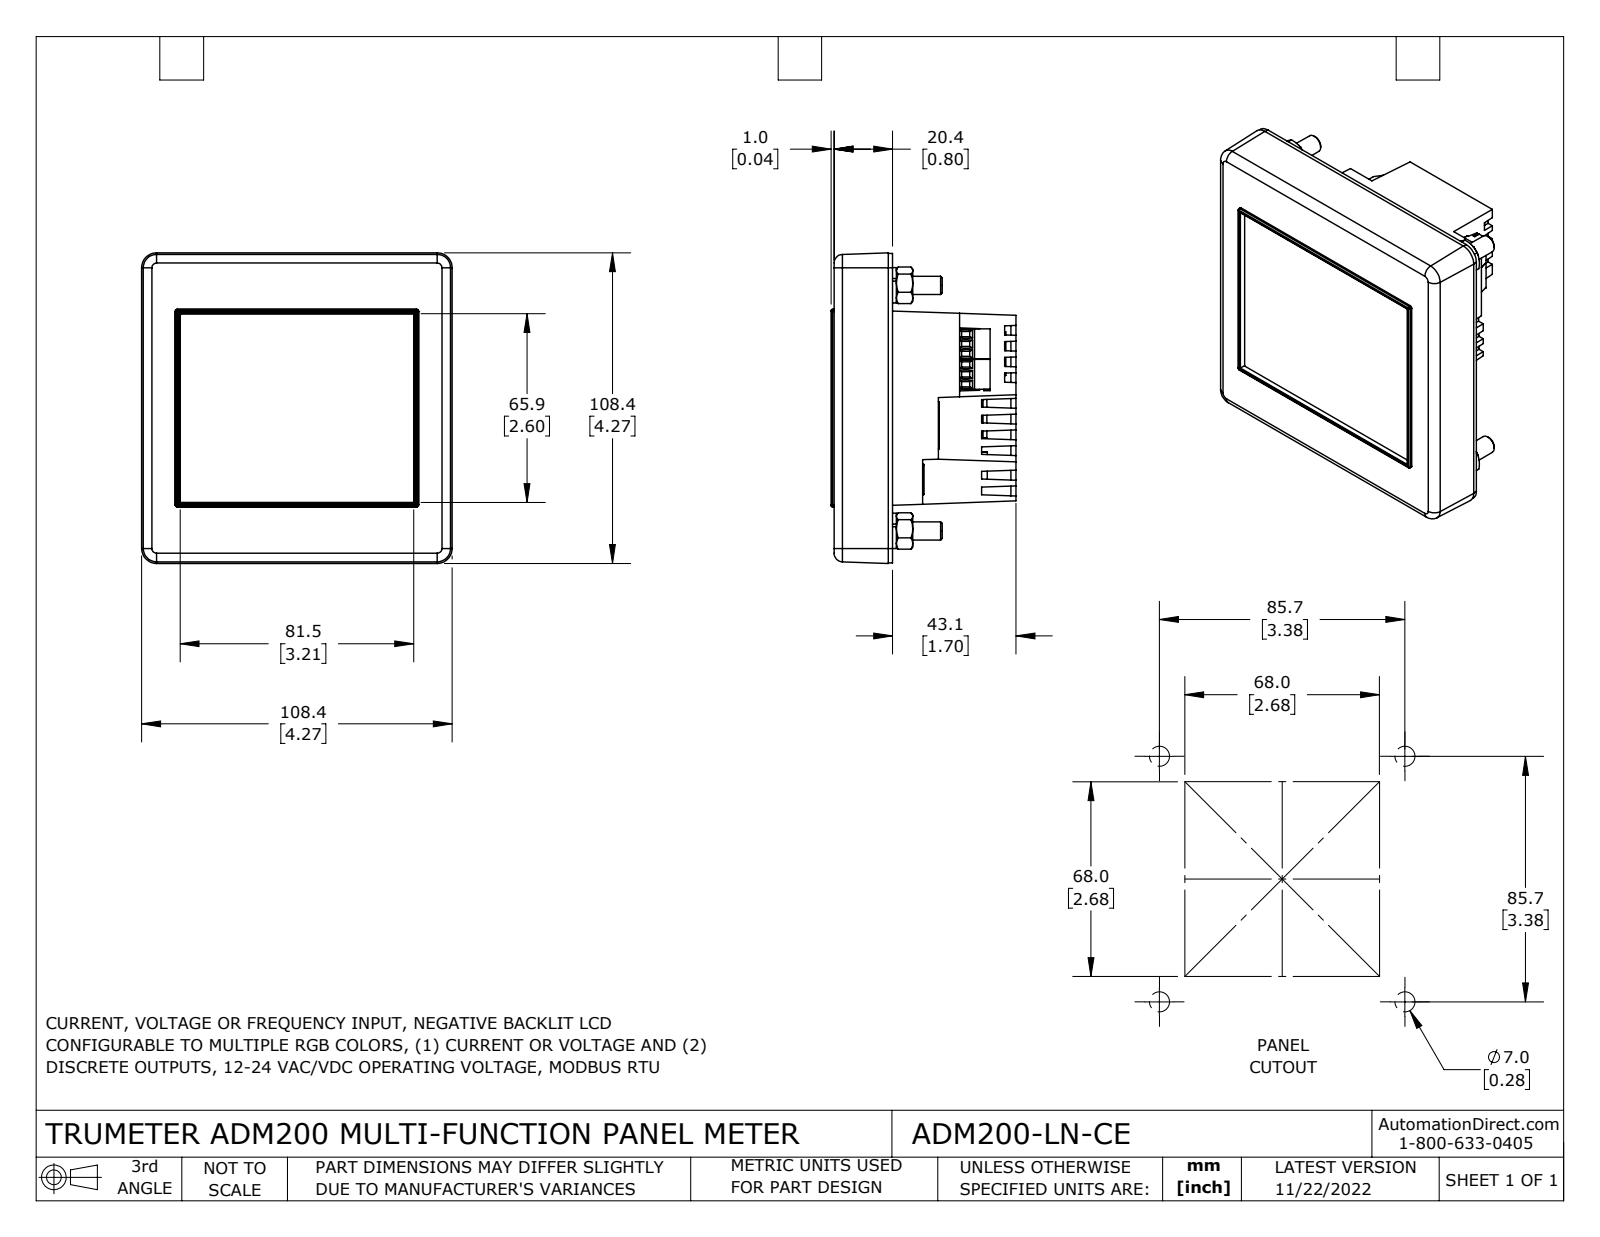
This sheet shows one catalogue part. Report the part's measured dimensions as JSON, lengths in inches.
{"part_name": "ADM200-LN-CE", "step_written_by": "SolidWorks 2021 (CONFIG_CONTROL_DESIGN)", "units": "inches", "bodies": {"solids": 23, "faces": 2059, "planar": 1384, "cylindrical": 290, "other": 385}, "overall_size": [4.269, 4.269, 2.541], "volume_in3": 7.808, "surface_area_in2": 190.8, "round_holes": [[0.071, 9], [0.114, 6], [0.118, 5], [0.213, 4], [0.25, 4], [0.26, 4], [0.295, 4], [0.154, 2]], "round_bosses_or_shafts": [[0.039, 5], [0.487, 4], [0.438, 4], [0.024, 4], [0.079, 2]], "partial_cylinders_radius": [[0.006, 32], [0.02, 30], [0.039, 7], [0.016, 4], [0.03, 4], [0.118, 4], [0.197, 4], [0.004, 2]], "face_to_face_distances": [0.031, 0.635, 0.11, 0.073, 0.059, 0.079, 0.694, 3.395, 3.468, 0.047], "hole_center_spacings": [0.709, 3.228, 0.136, 0.293, 0.986, 1.417, 2.126, 2.399]}
